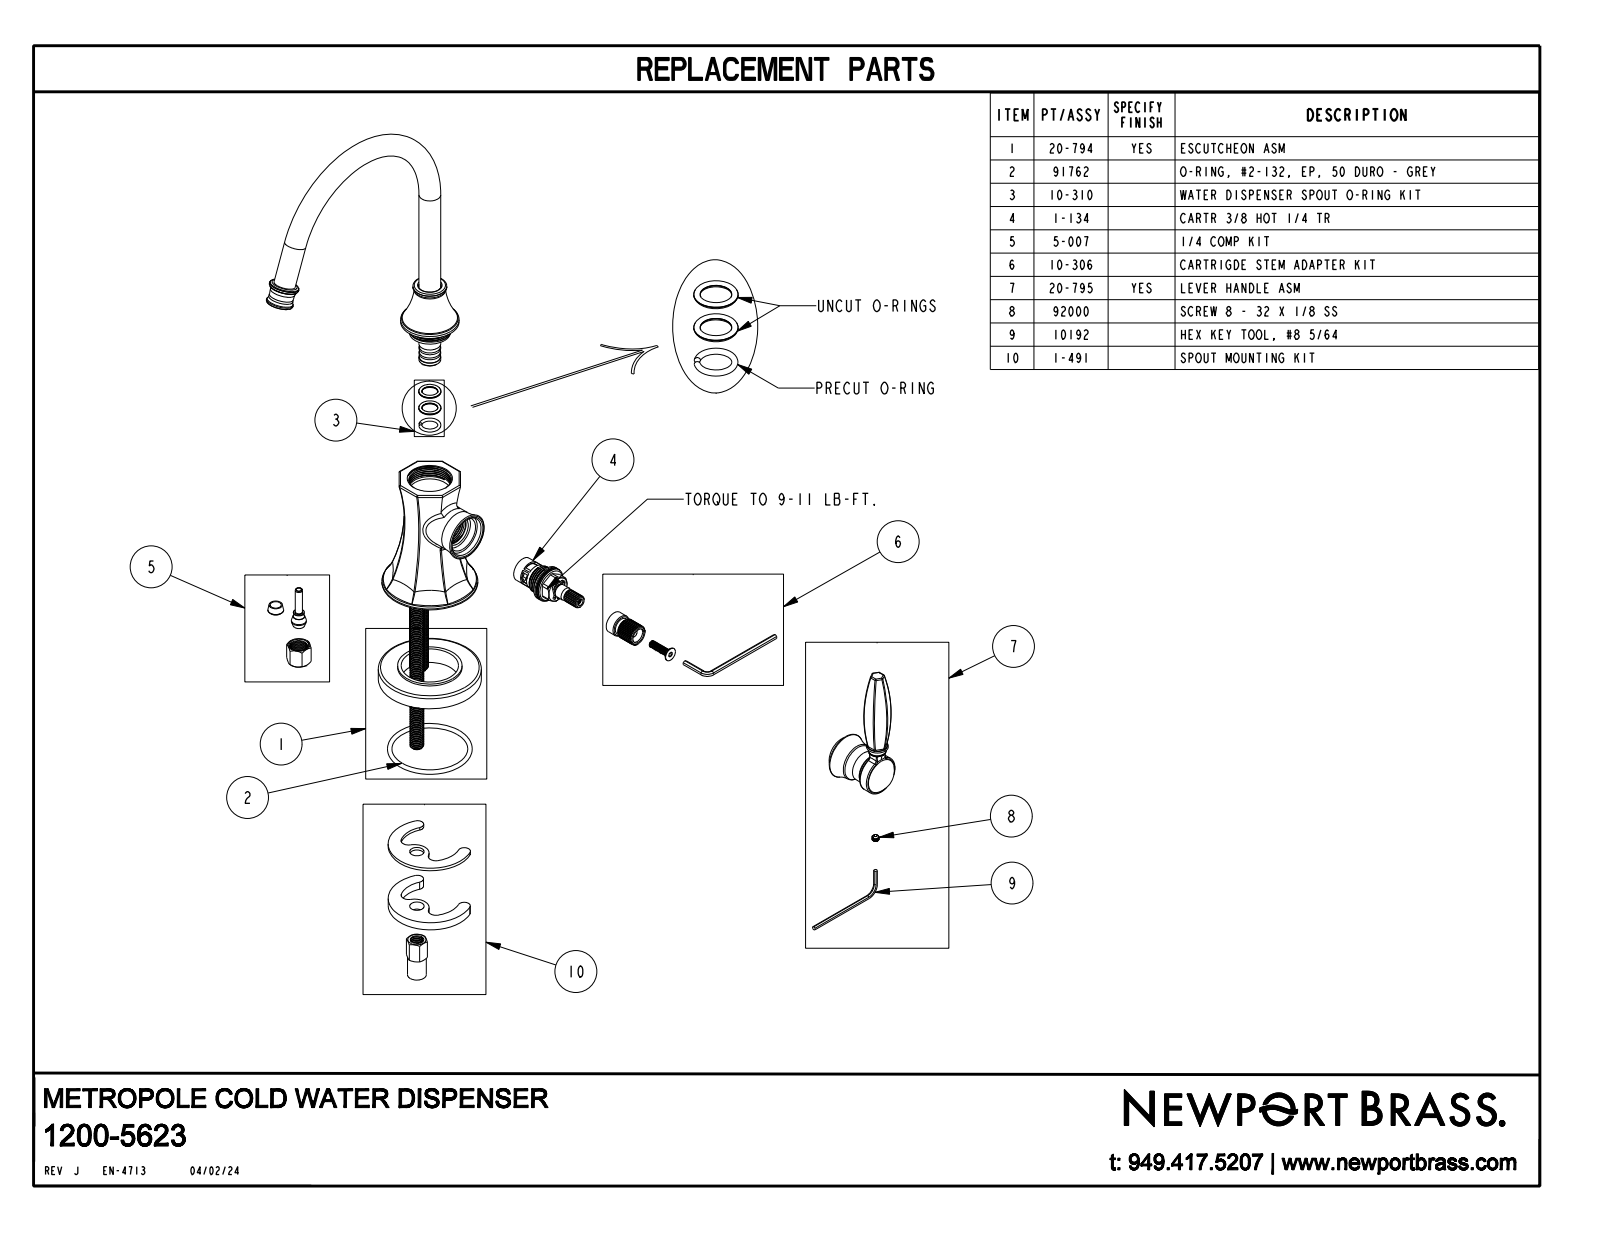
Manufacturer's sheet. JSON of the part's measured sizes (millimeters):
{"part_name": "1200-5623", "step_written_by": "CREO PARAMETRIC BY PTC INC, 2018400 (CONFIG_CONTROL_DESIGN)", "units": "millimeters", "bodies": {"solids": 1, "faces": 284, "planar": 15, "cylindrical": 15, "other": 254}, "overall_size": [256.3, 157.9, 95.3], "volume_mm3": 175700, "surface_area_mm2": 33300, "round_bosses_or_shafts": [[12.7, 2], [59.9, 1], [55.9, 1], [34, 1], [24.9, 1], [23.3, 1], [18.3, 1]], "face_to_face_distances": [8.4, 108.2, 99.8, 82.3, 73.9, 25.9, 11.2, 125.7, 117.3, 43.5]}
